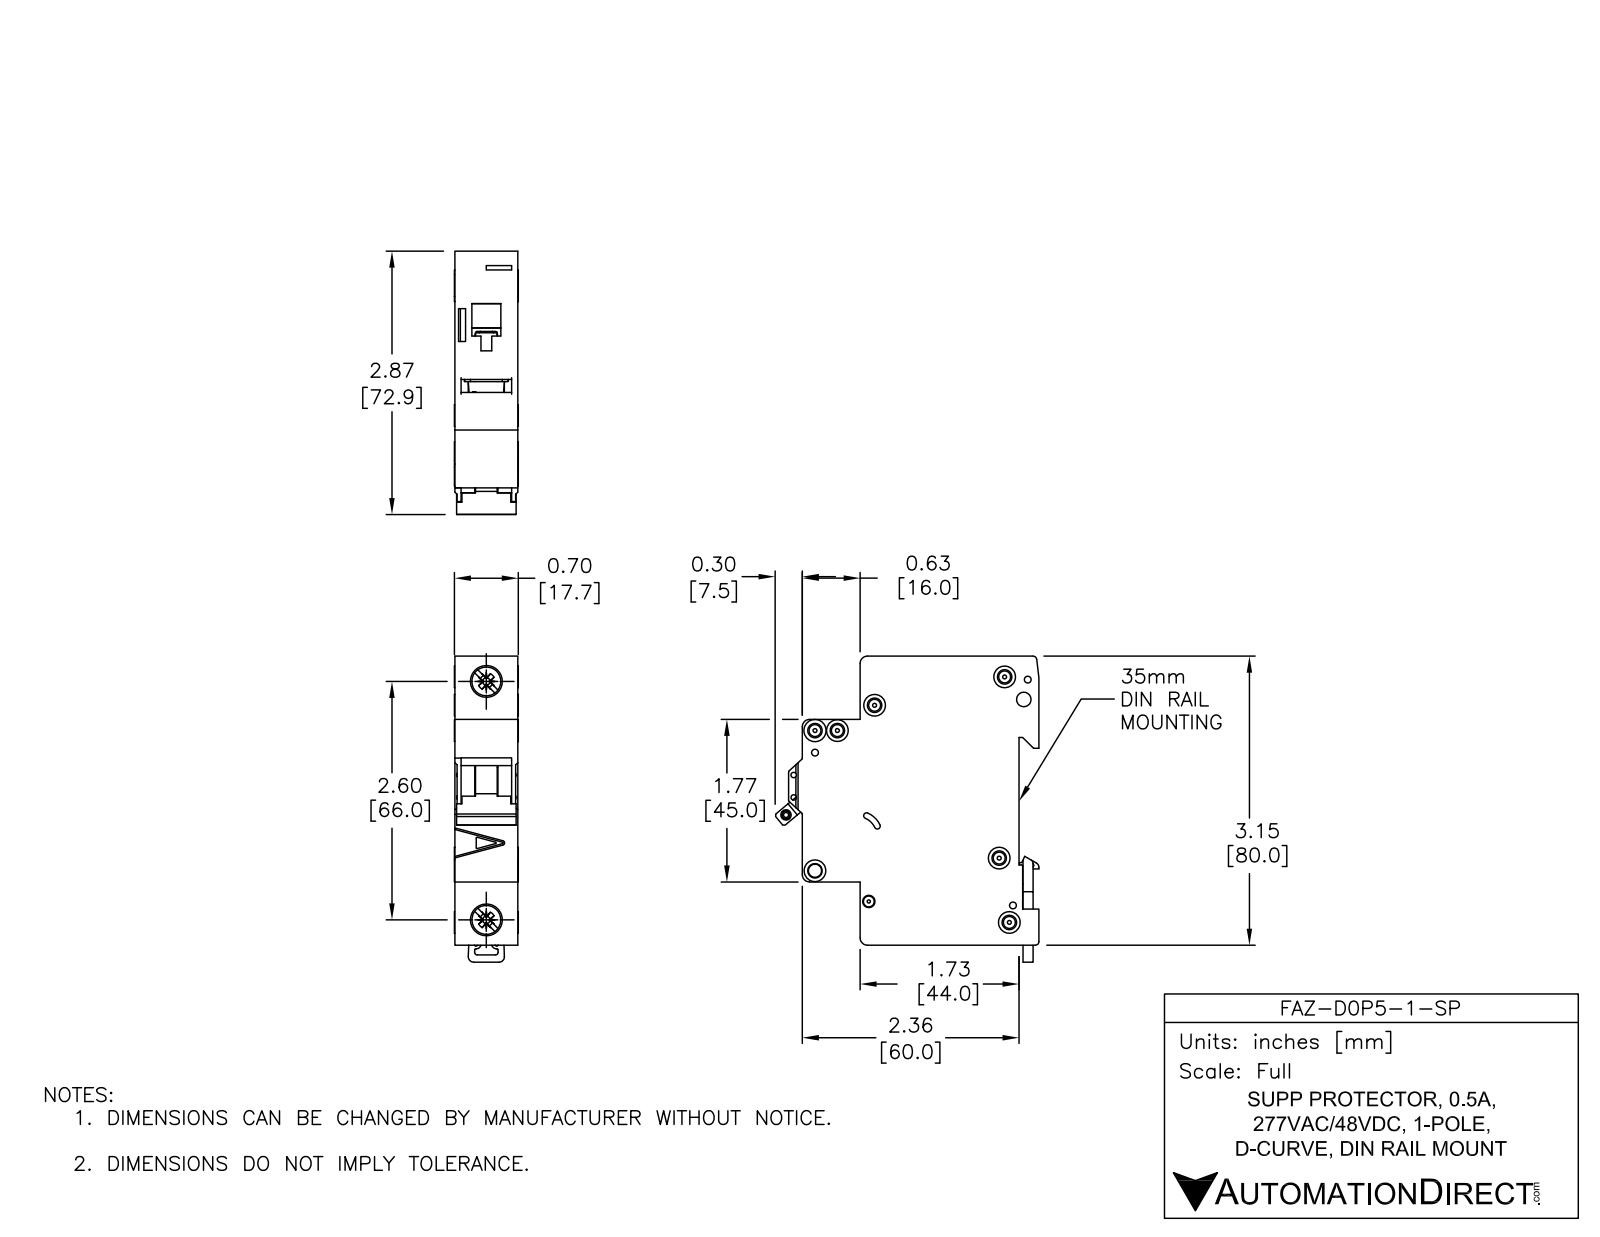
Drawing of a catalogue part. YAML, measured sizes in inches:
part_name: "FAZ-D0P5-1-SP"
step_written_by: "SolidWorks 2014 (AUTOMOTIVE_DESIGN)"
units: inches
bodies: {solids: 5, faces: 558, planar: 235, cylindrical: 202, other: 121}
overall_size: [3.338, 2.876, 0.697]
volume: 4.573
surface_area: 30.29
round_holes:
  - {diameter: 0.142, count: 6}
  - {diameter: 0.075, count: 3}
  - {diameter: 0.043, count: 2}
  - {diameter: 0.059, count: 2}
  - {diameter: 0.157, count: 2}
  - {diameter: 0.281, count: 2}
  - {diameter: 0.085, count: 1}
  - {diameter: 0.087, count: 1}
  - {diameter: 0.1, count: 1}
  - {diameter: 0.13, count: 1}
  - {diameter: 0.134, count: 1}
round_bosses_or_shafts:
  - {diameter: 0.236, count: 4}
  - {diameter: 0.323, count: 2}
  - {diameter: 0.098, count: 1}
partial_cylinders:
  - {radius: 0.01, count: 30}
  - {radius: 0.02, count: 13}
  - {radius: 0.079, count: 8}
  - {radius: 0.008, count: 5}
  - {radius: 0.039, count: 4}
  - {radius: 0.031, count: 2}
  - {radius: 0.118, count: 2}
  - {radius: 0.059, count: 1}
face_to_face_distances: [0.689, 3.129, 0.217, 1.949, 1.732, 2.579, 2.362, 0.63, 0.069, 0.62]
hole_center_spacings: [0.244, 0.537, 0.189, 0.204, 0.221, 0.24, 0.254, 0.322]
